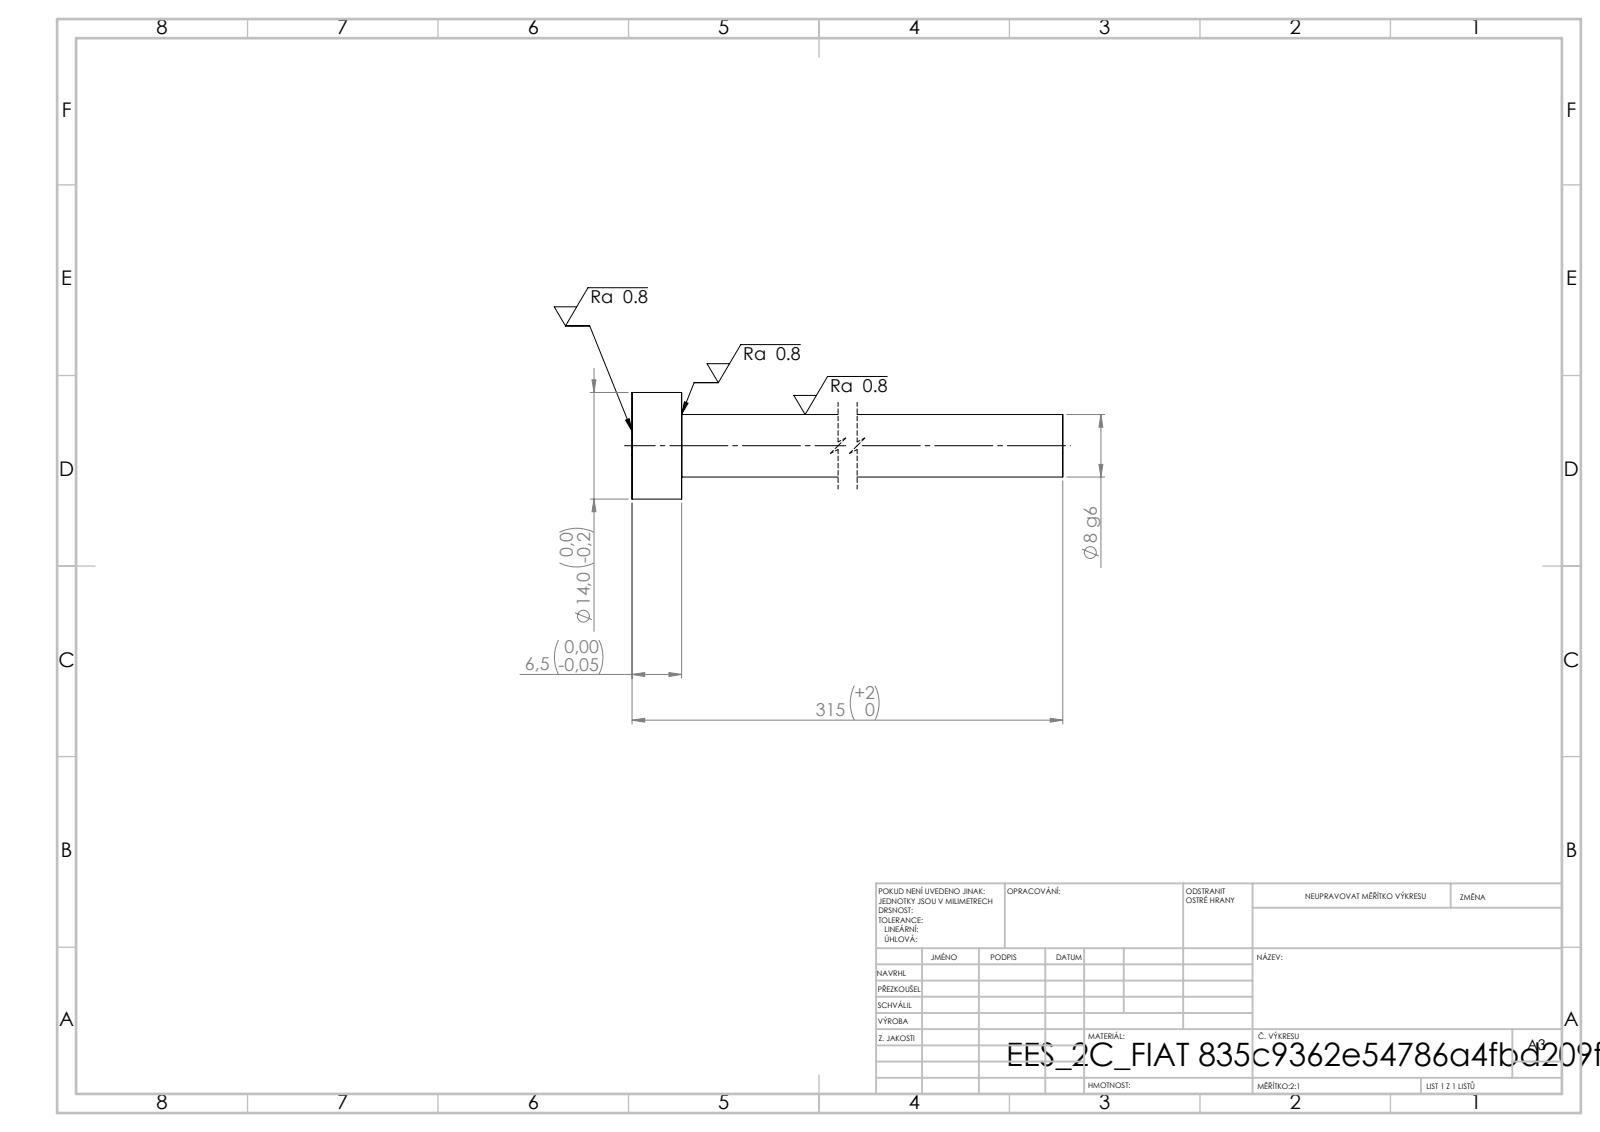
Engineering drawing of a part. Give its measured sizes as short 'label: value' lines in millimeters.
written by: SolidWorks 2019 (CONFIG_CONTROL_DESIGN)
unit: mm
bodies: 1 solid, 7 faces (3 planar, 4 cylindrical, 0 other)
size: 315 × 14 × 14
volume: 17 293 mm³; area: 8 541 mm²
bosses: 1× ⌀14, 1× ⌀8.2
face distances: 6.5, 315, 308.5
